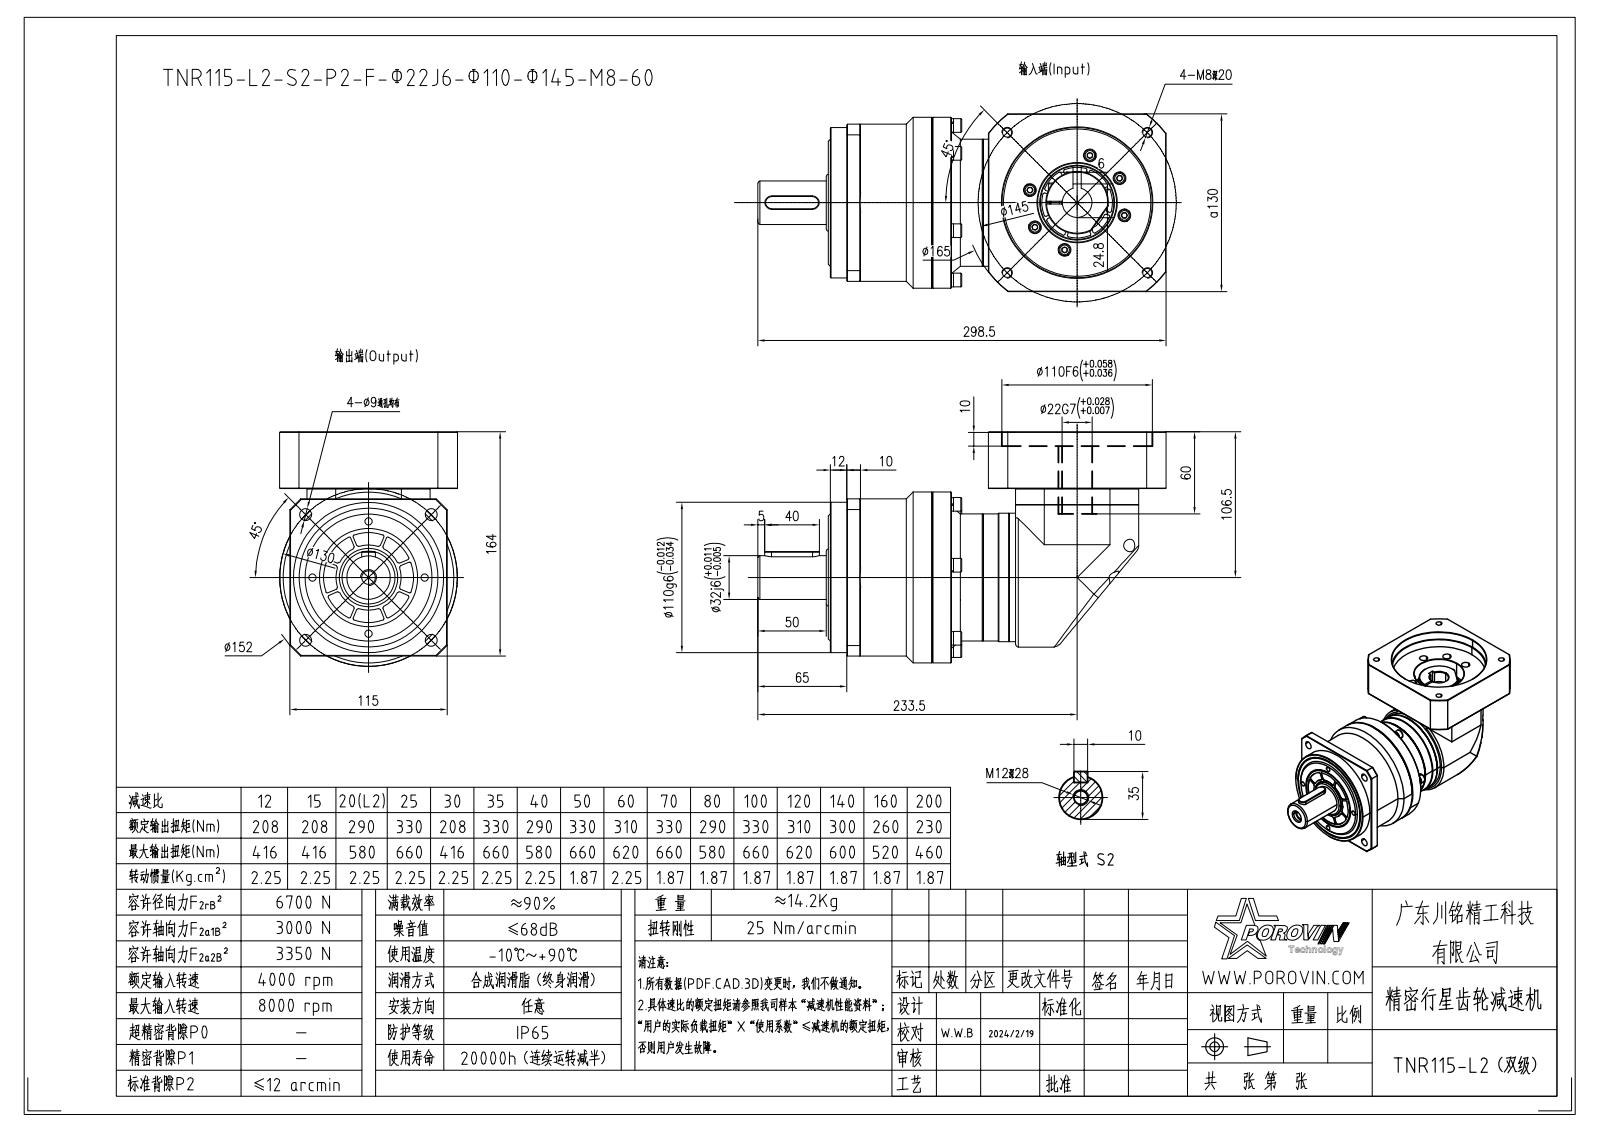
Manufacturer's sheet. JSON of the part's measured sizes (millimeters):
{"part_name": "20001_1_1; 5_5__5_5__1000_1_1; TN115_0001_ASM_1_ASM_1_ASM; HEXAGON_SOCKET_HEAD_CAP_SC-5945 (+8 more)", "step_written_by": "CREO PARAMETRIC BY PTC INC, 2020053 (CONFIG_CONTROL_DESIGN)", "units": "millimeters", "bodies": {"solids": 62, "faces": 1625, "planar": 680, "cylindrical": 645, "other": 300}, "overall_size": [298.5, 169, 130], "volume_mm3": 2486000, "surface_area_mm2": 319137, "round_holes": [[5.4, 19], [5.5, 17], [9.5, 12], [9.2, 7], [4.2, 6], [6.6, 6], [6.68, 6], [5, 5], [6.8, 4], [9, 4], [10.2, 2], [6.5, 1]], "round_bosses_or_shafts": [[8.5, 19], [8, 19], [5, 19], [10, 7], [6, 7], [9.88, 6], [125, 1], [115, 1]], "partial_cylinders_radius": [[1, 76], [5, 3], [4, 1], [5.25, 1], [51, 1], [76, 1], [82.5, 1]], "face_to_face_distances": [20, 37, 12, 56.5, 19.5, 56.3, 19.3, 130, 110, 21.5], "hole_center_spacings": [35.75, 57.25, 40.75, 46.18, 98.8, 39.08, 46.25, 58.16]}
